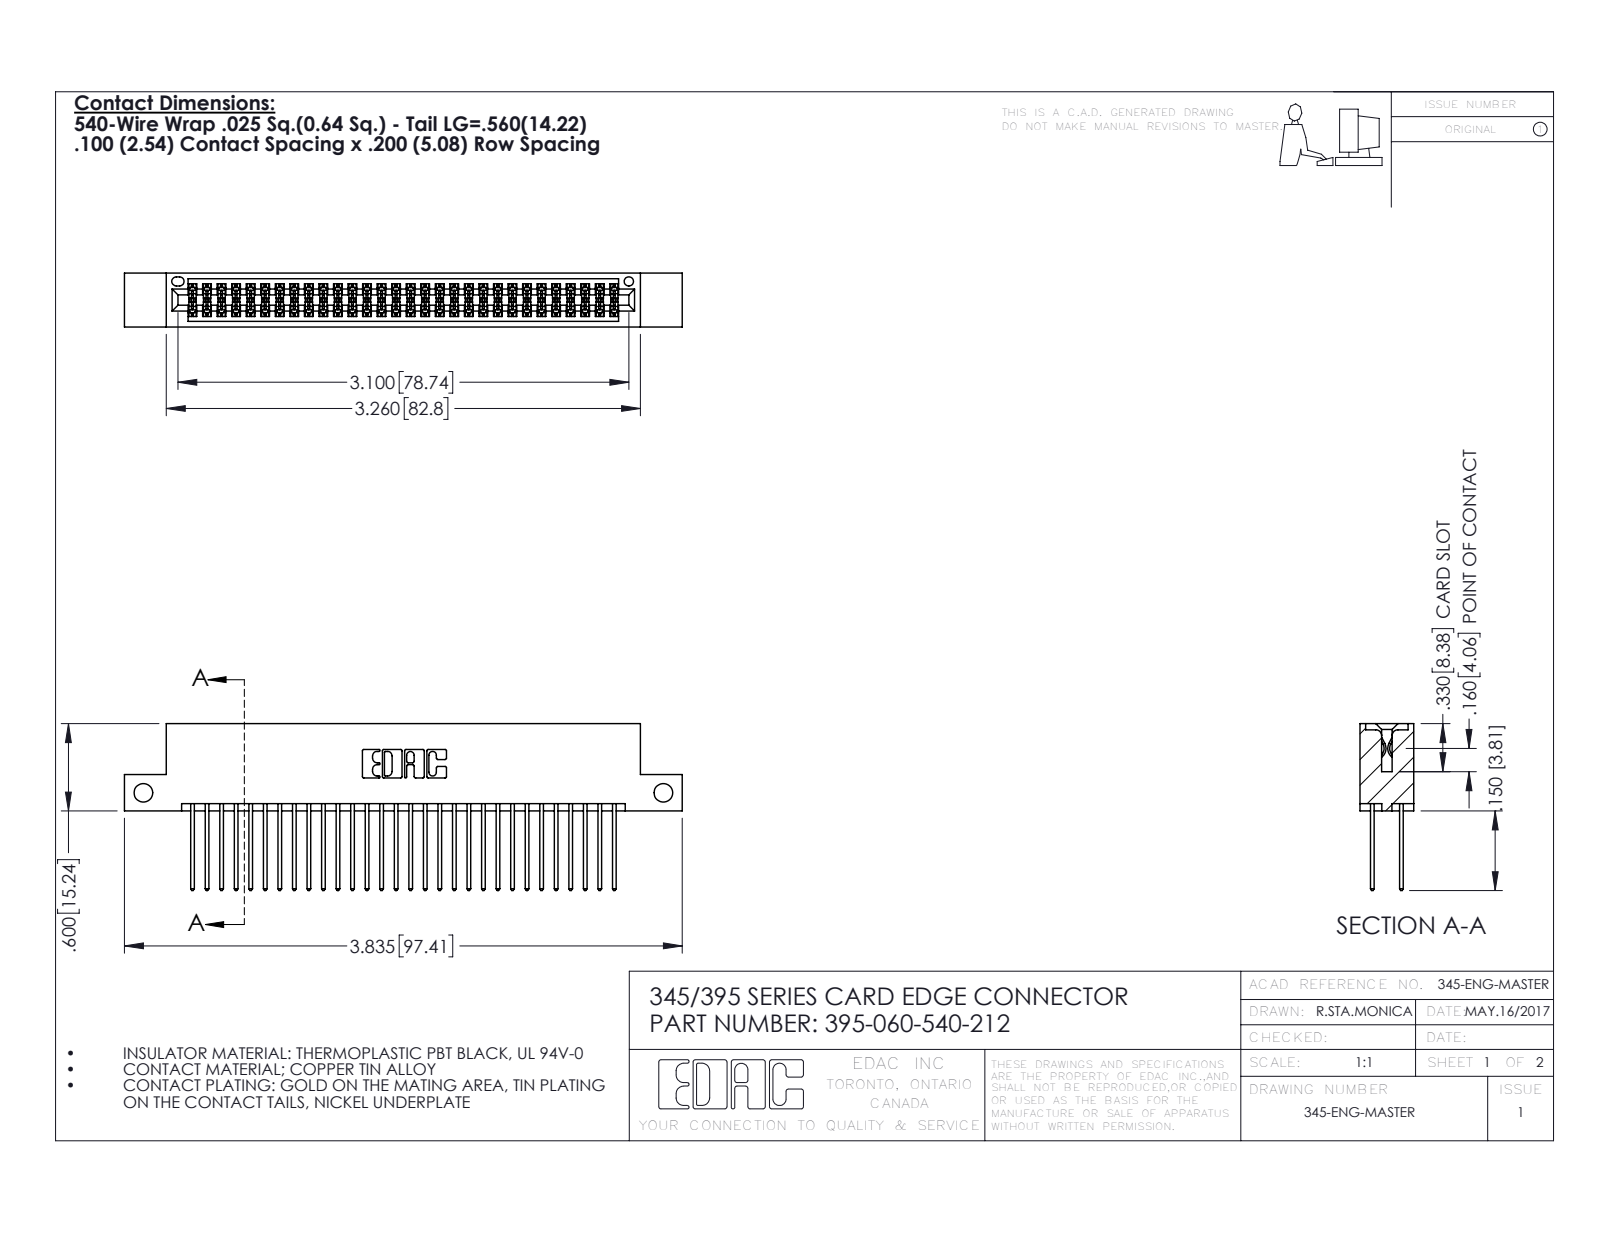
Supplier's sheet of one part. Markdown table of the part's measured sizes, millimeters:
| quantity | value |
| --- | --- |
| part name | 345 Part_Flush Mounting Lugs - Side Mount; 395-060-540-212; 345-292-001_345-293-140 |
| STEP written by | SolidWorks 2016 (CONFIG_CONTROL_DESIGN) |
| units | millimeters |
| bodies | 61 solids, 3126 faces (2060 planar, 1066 cylindrical, 0 other) |
| overall size | 97.4 × 29.1 × 9.4 |
| volume | 9 490 mm³ |
| surface area | 14 720 mm² |
| round holes (diameter × count) | 3.3 × 2, 1.6 × 1 |
| partial cylindrical surfaces (radius × count) | 0.2 × 90, 0.3 × 60, 0.3 × 22, 0.2 × 6, 0.8 × 6, 0.7 × 3, 0.4 × 2, 0.5 × 2 |
| main face-to-face distances | 7.6, 1.8, 5.1, 2.5, 6.9, 0.6, 9.4, 5.7, 4.4, 3.8 |
| hole center spacings | 90.8 |
